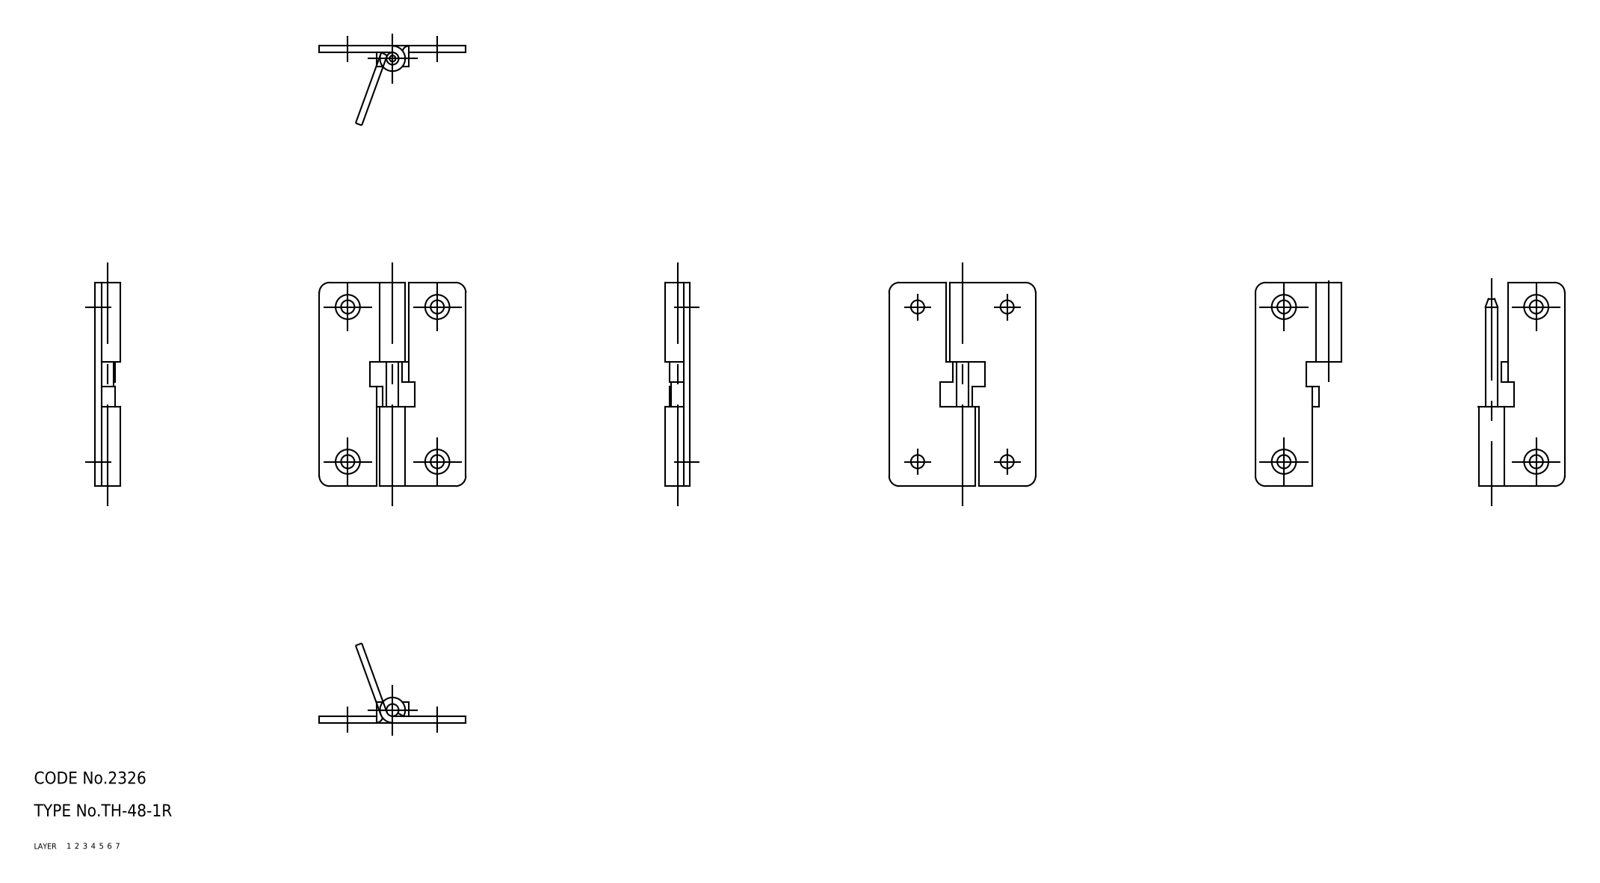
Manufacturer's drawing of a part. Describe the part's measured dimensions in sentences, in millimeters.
The part is named "shaft; hinge piece_B; hinge piece_A; TH_48_1R_18745_36". Its 3-D file was written by "CADfix (AUTOMOTIVE_DESIGN)". It is 3 solids with 60 faces: 0 planar, 0 cylindrical and 60 other. Overall it measures 50 by 36 by 6.2 millimeters. Its volume is 3 489 cubic millimeters and its surface area 5 049 square millimeters.
